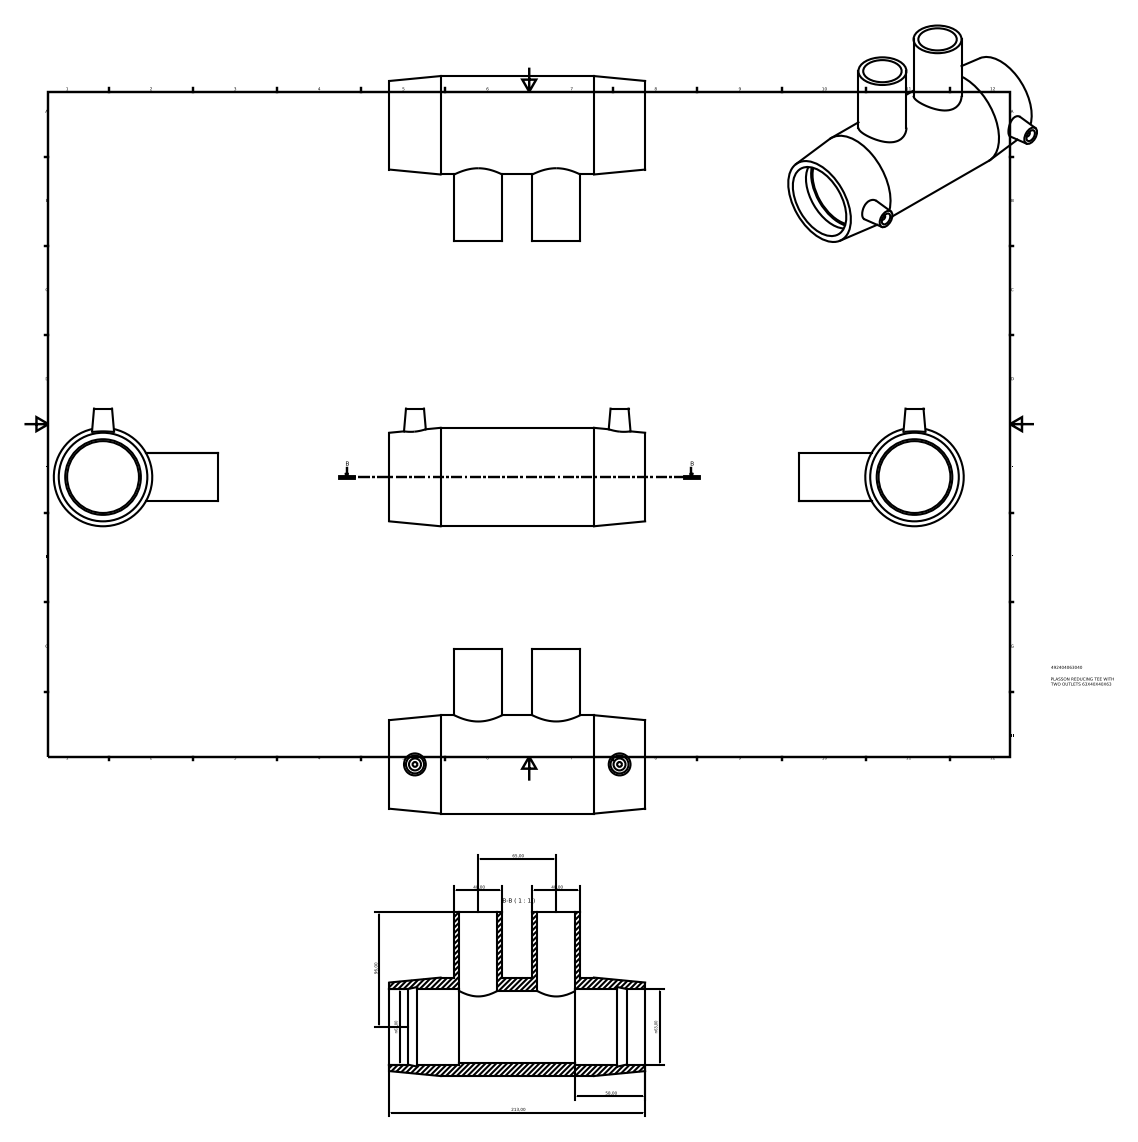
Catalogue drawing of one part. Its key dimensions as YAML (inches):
part_name: "492404063040"
step_written_by: "Autodesk Inventor 2015 (AUTOMOTIVE_DESIGN)"
units: inches
bodies: {solids: 1, faces: 35, planar: 14, cylindrical: 15, other: 6}
overall_size: [8.386, 5.394, 3.858]
volume: 29.53
surface_area: 196.2
round_holes:
  - {diameter: 0.394, count: 2}
  - {diameter: 1.26, count: 2}
  - {diameter: 2.356, count: 1}
  - {diameter: 2.48, count: 1}
round_bosses_or_shafts:
  - {diameter: 1.575, count: 2}
  - {diameter: 0.157, count: 2}
  - {diameter: 3.228, count: 1}
face_to_face_distances: [8.386, 0.913, 7.472, 2.283, 6.102, 1.37, 5.189, 6.559, 3.819, 0.551]
hole_center_spacings: [2.559, 6.709]
